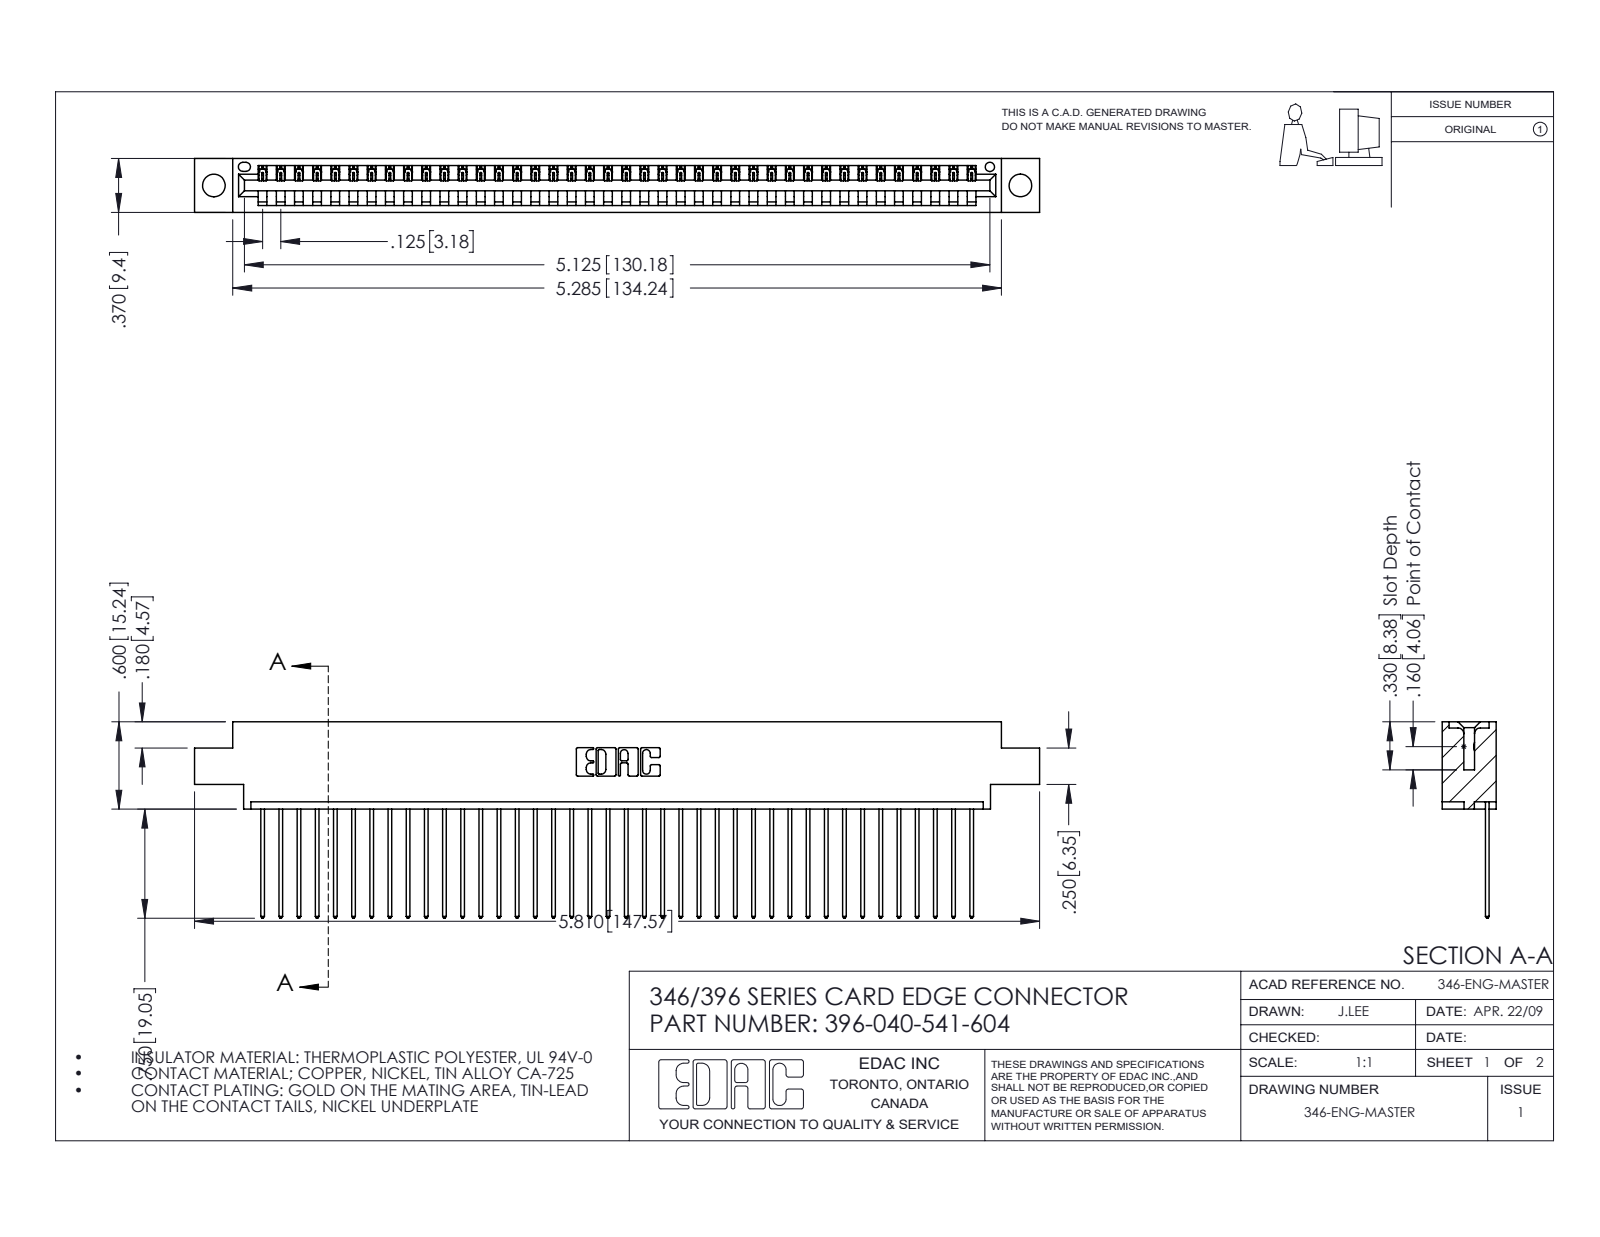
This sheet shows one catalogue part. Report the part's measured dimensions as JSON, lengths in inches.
{"part_name": "346 Part_0.170 Offset - 0.156 Dia-TH; 345-292-001_345-293-141; 396-040-541-604", "step_written_by": "SolidWorks 2016 (CONFIG_CONTROL_DESIGN)", "units": "inches", "bodies": {"solids": 41, "faces": 2446, "planar": 1680, "cylindrical": 766, "other": 0}, "overall_size": [5.81, 1.35, 0.37], "volume_in3": 0.854, "surface_area_in2": 28.26, "round_holes": [[0.156, 2], [0.064, 1]], "partial_cylinders_radius": [[0.006, 80], [0.01, 80], [0.01, 22], [0.007, 6], [0.031, 6], [0.026, 3], [0.031, 2], [0.04, 2]], "face_to_face_distances": [0.048, 0.322, 0.37, 0.25, 0.072, 0.298, 0.025, 0.148, 0.222, 0.1], "hole_center_spacings": [0.246, 5.336, 5.545]}
